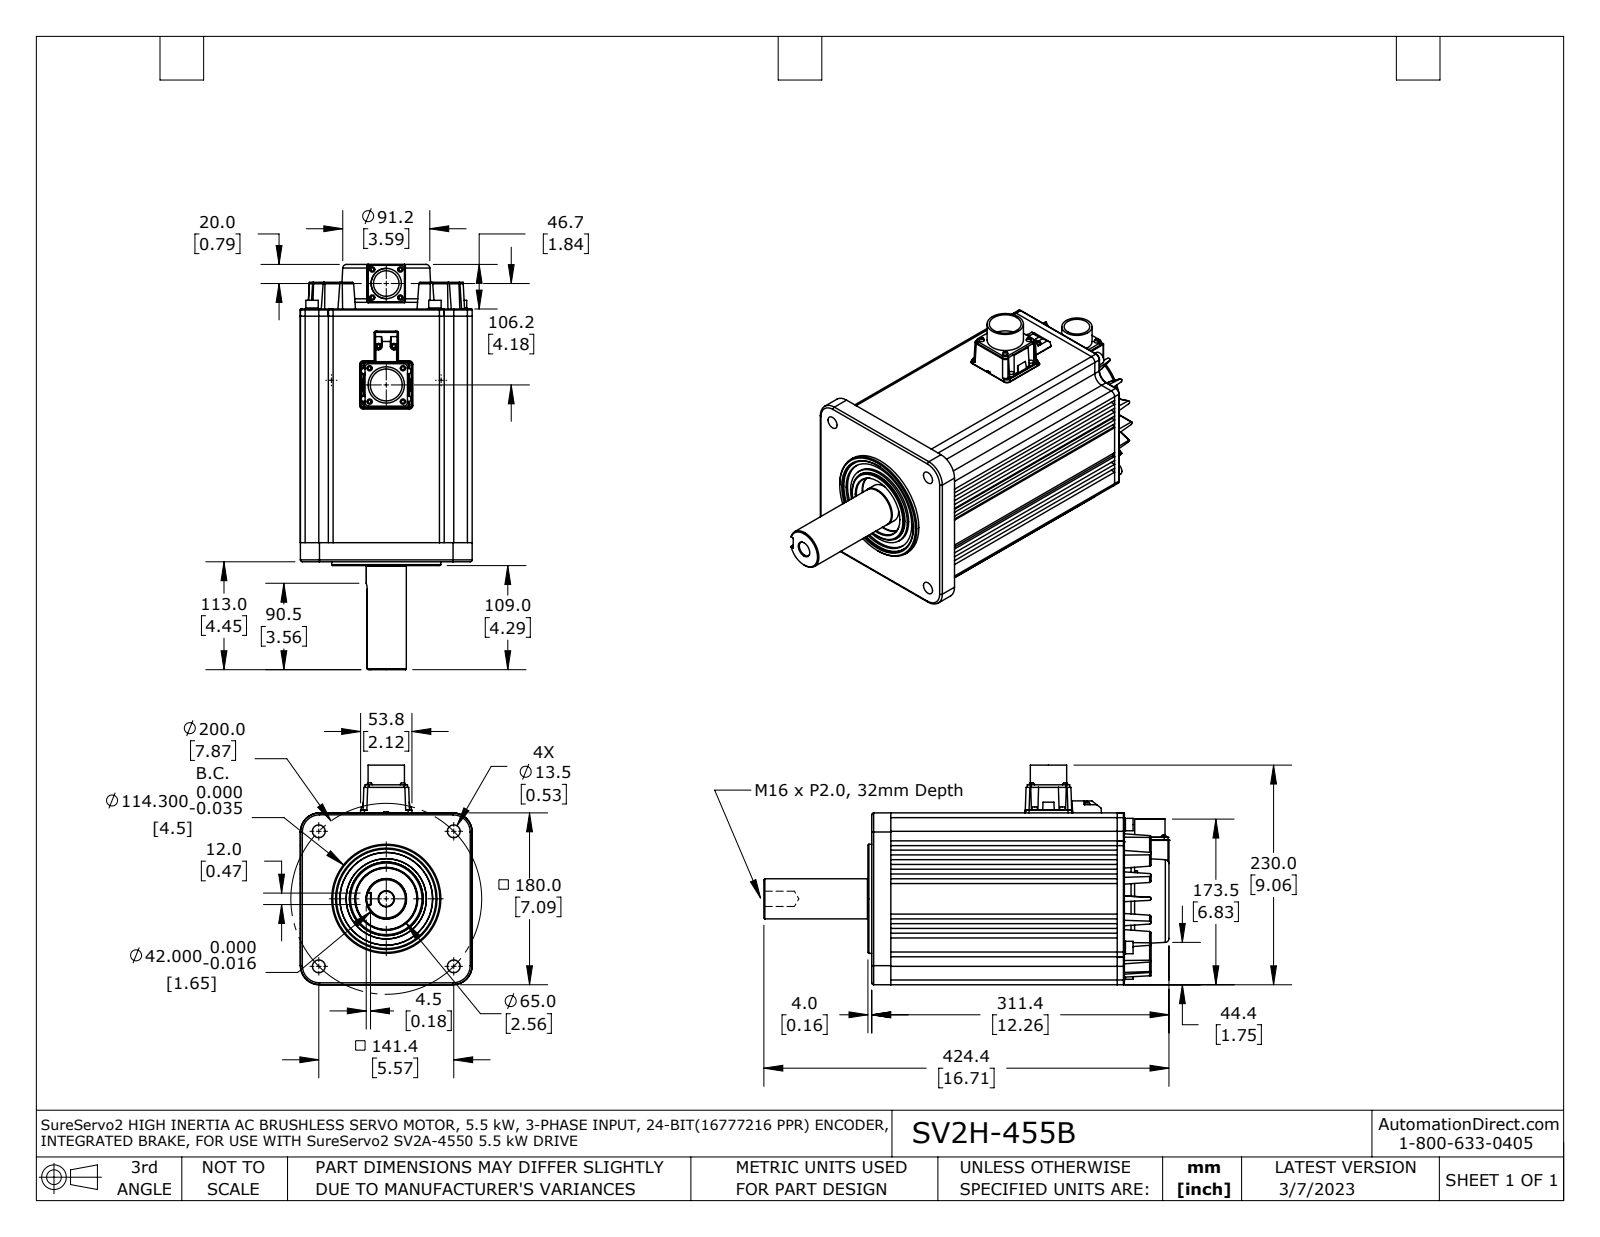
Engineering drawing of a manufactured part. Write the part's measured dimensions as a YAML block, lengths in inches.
part_name: "SV2H-455B"
step_written_by: "SolidWorks 2021 (AUTOMOTIVE_DESIGN)"
units: inches
bodies: {solids: 1, faces: 613, planar: 326, cylindrical: 188, other: 99}
overall_size: [16.709, 9.056, 7.087]
volume: 502.5
surface_area: 611.5
round_holes:
  - {diameter: 0.531, count: 4}
  - {diameter: 0.315, count: 2}
  - {diameter: 0.63, count: 1}
  - {diameter: 1.058, count: 1}
  - {diameter: 1.317, count: 1}
  - {diameter: 2.559, count: 1}
round_bosses_or_shafts:
  - {diameter: 0.217, count: 7}
  - {diameter: 0.528, count: 4}
  - {diameter: 0.512, count: 4}
  - {diameter: 0.236, count: 2}
  - {diameter: 4.567, count: 1}
  - {diameter: 4.5, count: 1}
  - {diameter: 1.673, count: 1}
  - {diameter: 1.654, count: 1}
partial_cylinders:
  - {radius: 0.064, count: 16}
  - {radius: 0.157, count: 16}
  - {radius: 0.197, count: 16}
  - {radius: 0.039, count: 12}
  - {radius: 0.02, count: 8}
  - {radius: 0.079, count: 6}
  - {radius: 0.15, count: 4}
  - {radius: 0.394, count: 4}
face_to_face_distances: [0.197, 0.394, 7.087, 1.154, 5.933, 0.591, 3.031, 3.228, 2.835, 0.787]
hole_center_spacings: [3.937, 5.568, 0.824, 3.661, 4.8, 5.897, 7.559, 7.874]
